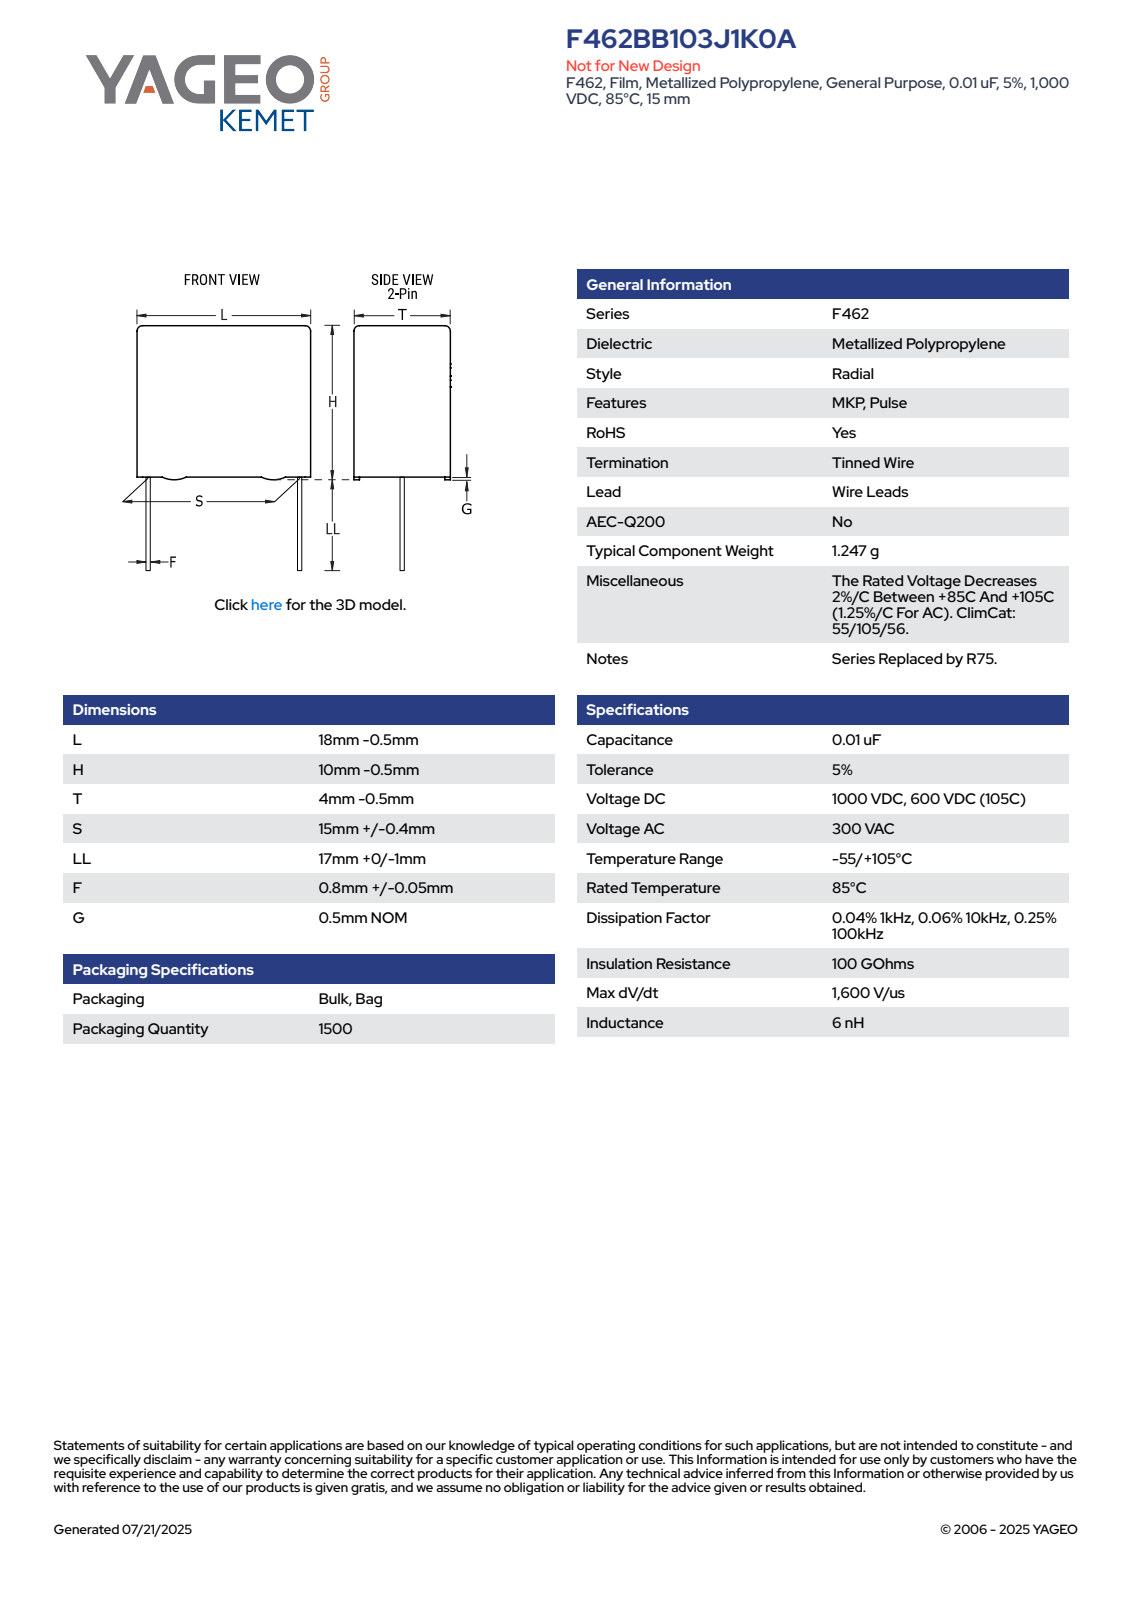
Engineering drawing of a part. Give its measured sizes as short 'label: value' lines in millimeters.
name: CFR_RBG_18X10X4_L17.5H9.5T3.5S15LL17F0.85G0.5
written by: SolidWorks 2014 (AUTOMOTIVE_DESIGN)
unit: mm
bodies: 4 solids, 89 faces (81 planar, 8 cylindrical, 0 other)
size: 26.5 × 17.5 × 3.5
volume: 570 mm³; area: 630 mm²
bosses: 2× ⌀0.85
rounds: 4× R0.5
face distances: 3.5, 9, 17.5, 3.3, 3.1, 0.5, 9.5, 17, 26.5, 8.83
